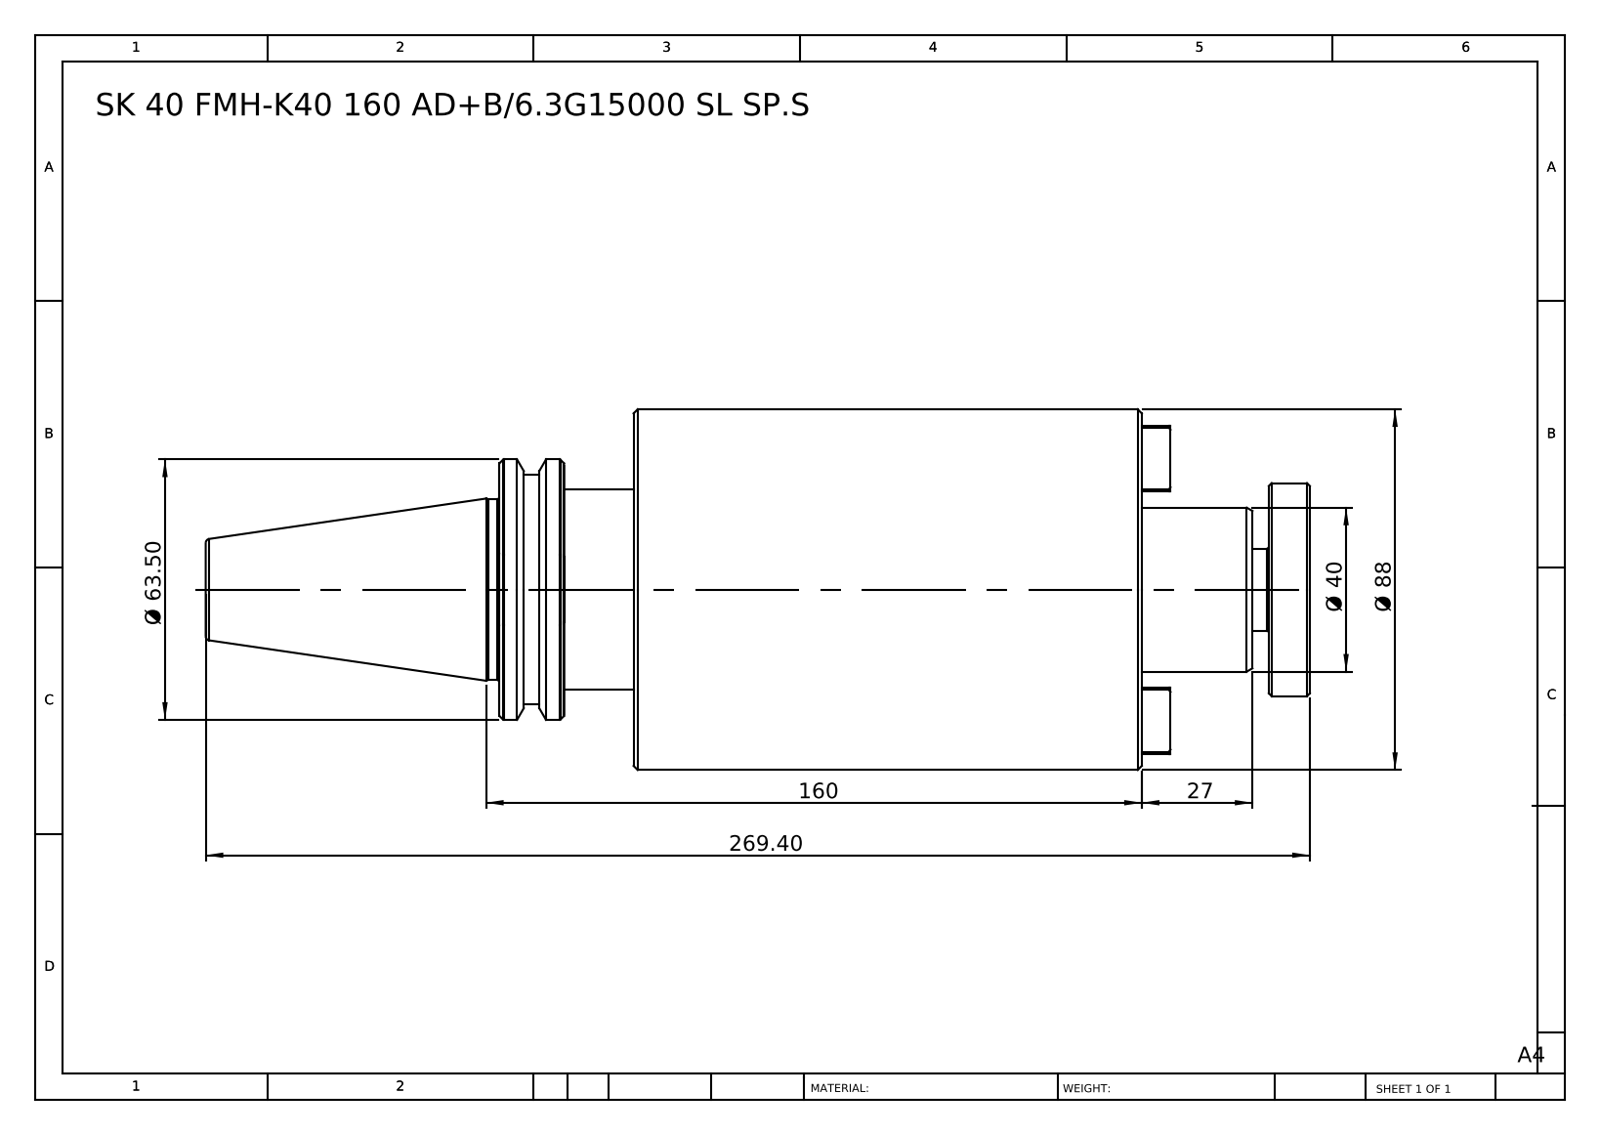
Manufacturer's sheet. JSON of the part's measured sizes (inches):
{"part_name": "SK40 FMH40 160 AD-6.3G15000 SL SP.S", "step_written_by": "SolidWorks 2014 (CONFIG_CONTROL_DESIGN)", "units": "inches", "bodies": {"solids": 1, "faces": 110, "planar": 36, "cylindrical": 18, "other": 56}, "overall_size": [10.606, 3.465, 3.465], "volume_in3": 58.75, "surface_area_in2": 110.7, "round_bosses_or_shafts": [[3.465, 1], [2.5, 1], [2.205, 1], [2.047, 1], [1.929, 1], [1.732, 1], [1.575, 1], [0.787, 1]], "face_to_face_distances": [4.882, 1.614, 6.496, 0.394, 1.22, 6.102, 7.787, 7.394, 6.173, 1.291]}
